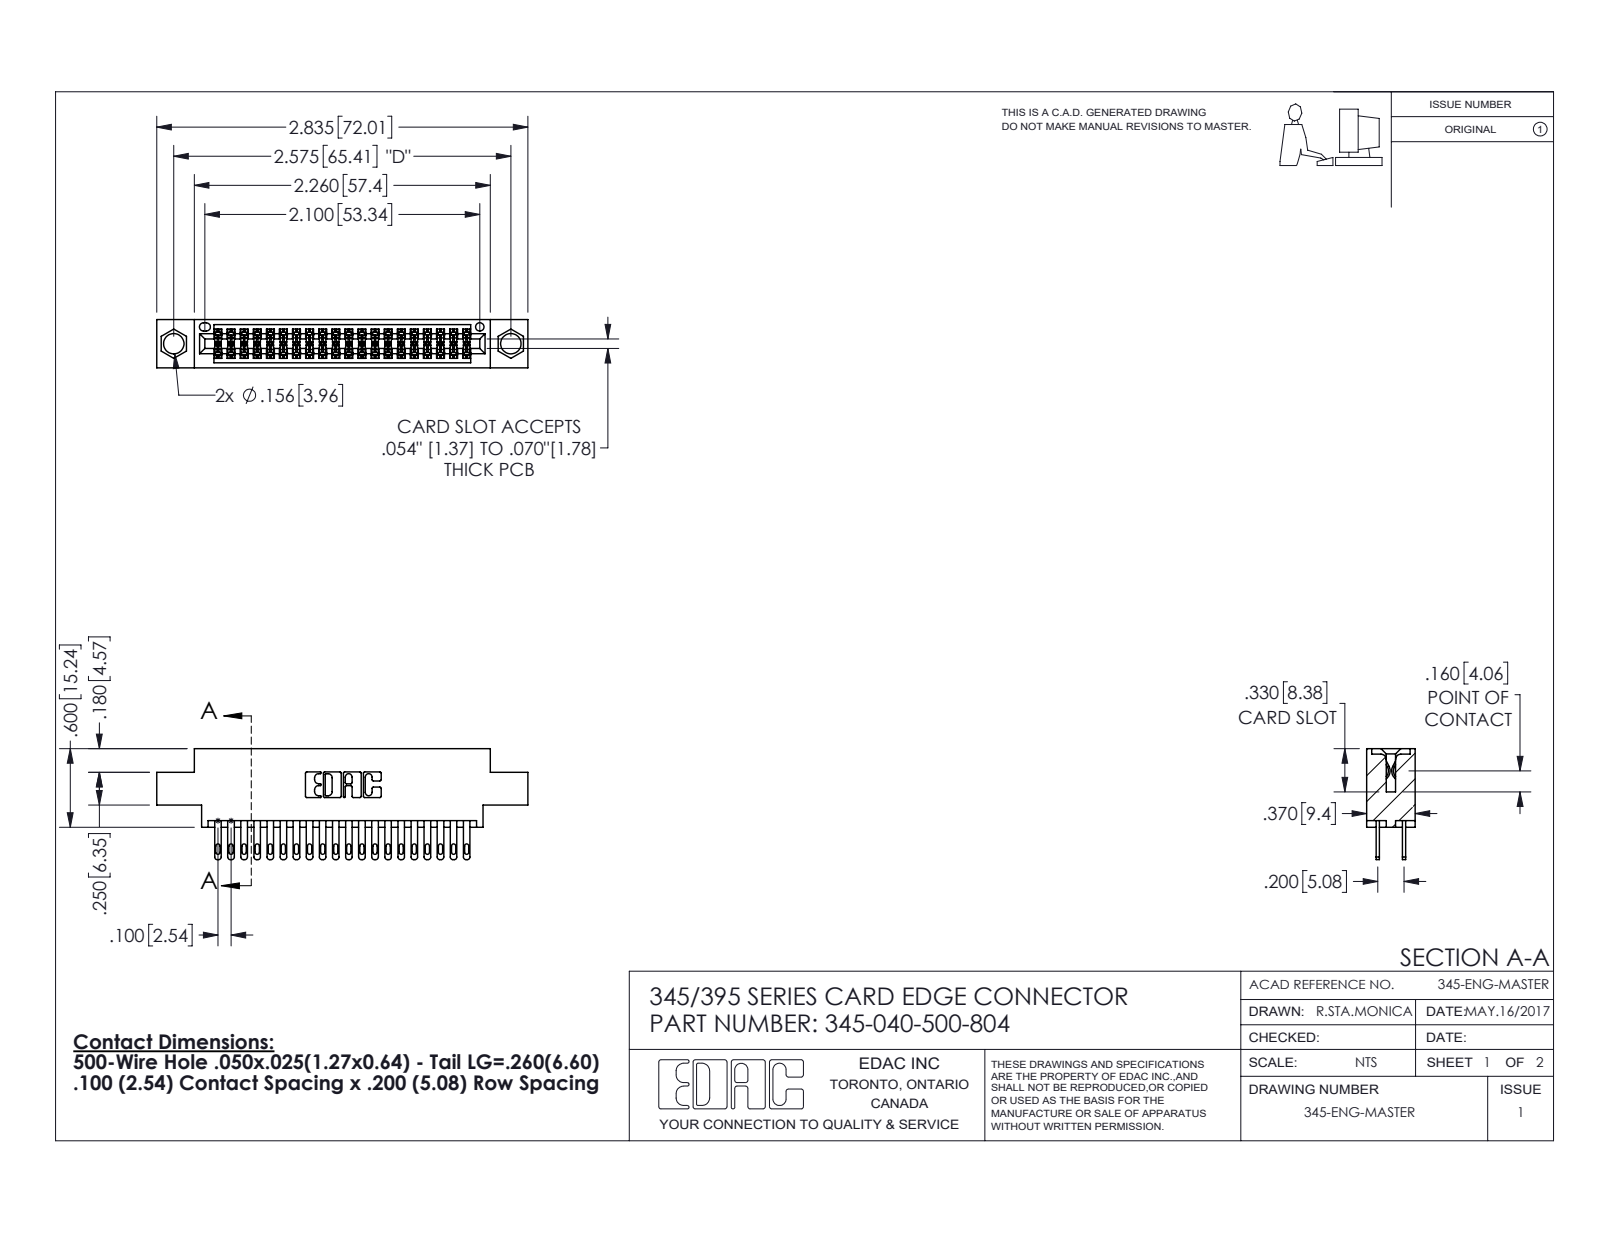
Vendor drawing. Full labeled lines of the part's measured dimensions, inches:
Part name (STEP PRODUCT): 345-040-500-804; 345 Part_0.170 Offset - 0.156 Dia-TI; 345-292-001_345-293-100
STEP written by: SolidWorks 2020 (CONFIG_CONTROL_DESIGN)
Units: inches
Bodies: 41 solids, 1984 faces (1178 planar, 806 cylindrical, 0 other)
Overall size (bounding box): 2.835 × 0.847 × 0.37
Volume: 0.408 in³ · Surface area: 15.3 in²
Round holes (diameter × count): ⌀0.156 ×2, ⌀0.064 ×1
Partial cylindrical surfaces — rounded edges, fillets, slot ends (radius × count): R0.006 ×60, R0.016 ×40, R0.02 ×40, R0.01 ×22, R0.007 ×6, R0.031 ×6, R0.026 ×3, R0.014 ×2
Main face-to-face distances: 0.072, 0.298, 0.2, 0.098, 0.272, 0.025, 0.37, 0.225, 0.175, 0.15
Hole centre spacings: 0.27, 2.341, 2.575
